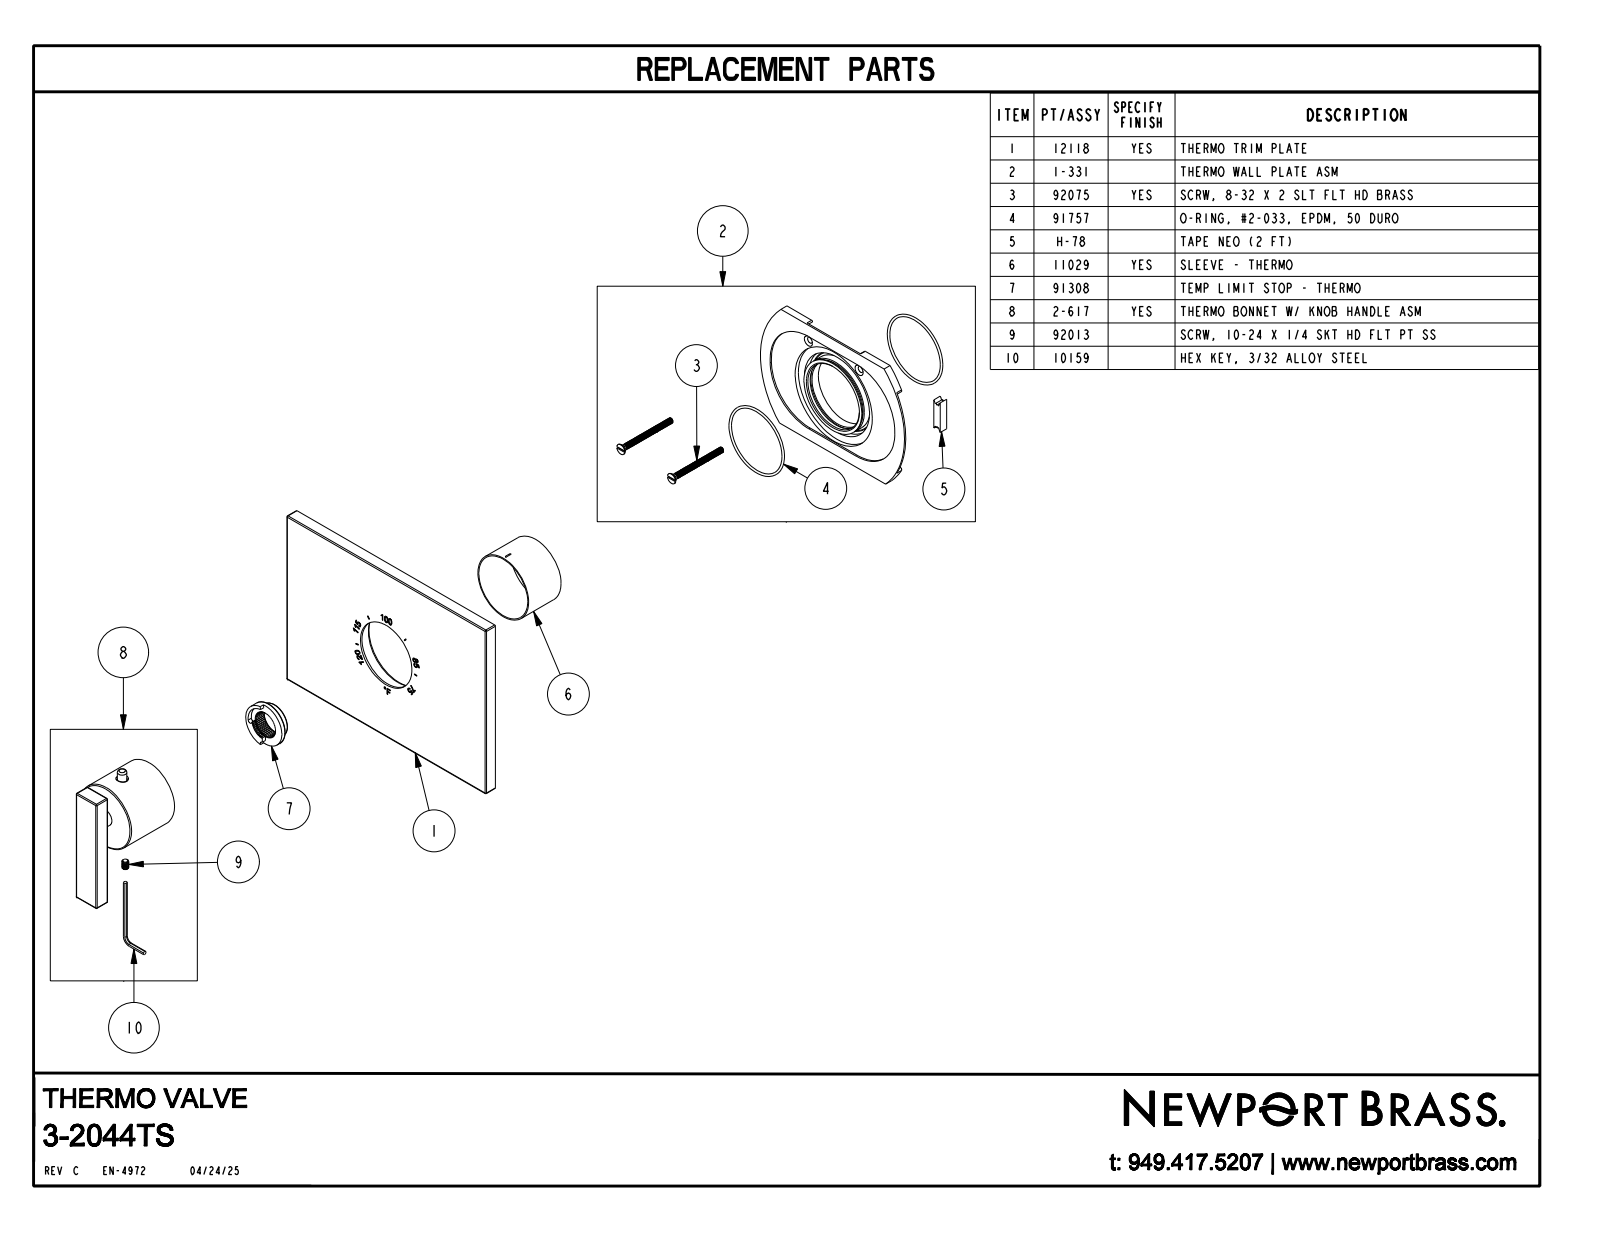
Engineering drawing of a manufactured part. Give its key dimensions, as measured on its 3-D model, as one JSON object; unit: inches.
{"part_name": "3-2044TS", "step_written_by": "CREO PARAMETRIC BY PTC INC, 2018400 (CONFIG_CONTROL_DESIGN)", "units": "inches", "bodies": {"solids": 1, "faces": 334, "planar": 114, "cylindrical": 28, "other": 192}, "overall_size": [7.75, 5.5, 2.876], "volume_in3": 22.63, "surface_area_in2": 115.1, "round_holes": [[0.063, 1]], "round_bosses_or_shafts": [[1.97, 1], [0.5, 1], [0.031, 1]], "partial_cylinders_radius": [[0.03, 20]], "face_to_face_distances": [0.375, 3.475, 4.275, 2.126, 1.751, 5.5, 2.876, 2.501, 0.75, 2.426]}
